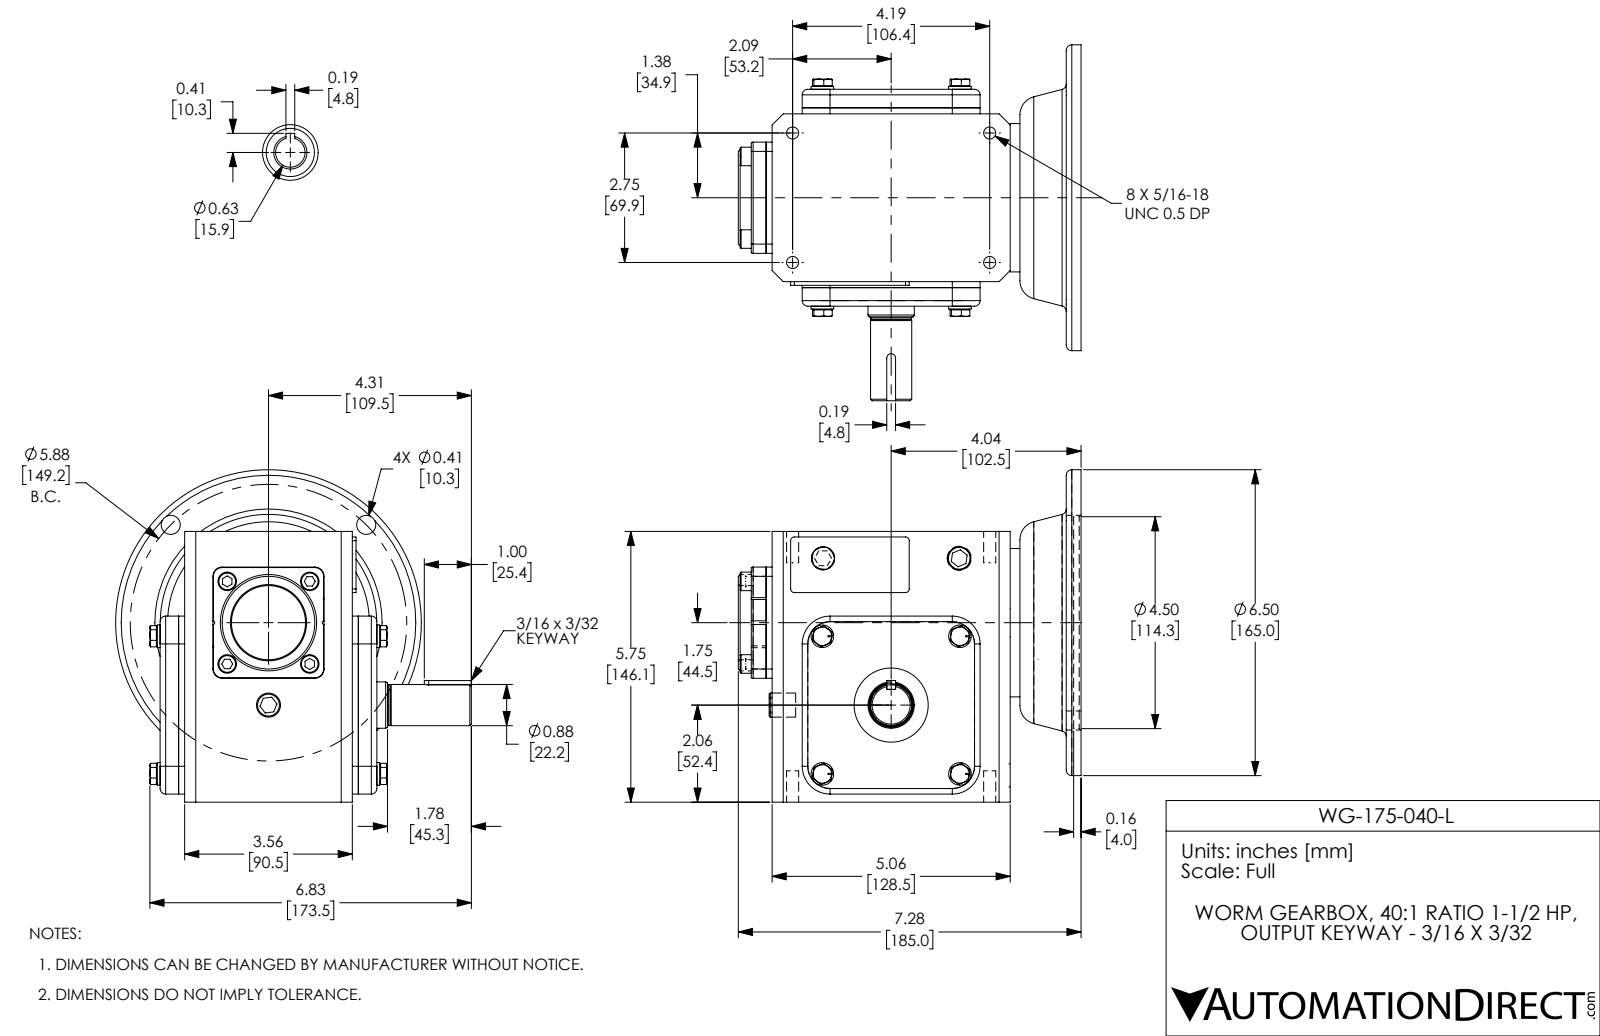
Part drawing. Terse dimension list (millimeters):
name: WG-175-040-L
written by: SolidWorks 2017 (AUTOMOTIVE_DESIGN)
unit: mm
bodies: 43 solids, 613 faces (312 planar, 172 cylindrical, 129 other)
size: 192 × 185 × 179.3
volume: 2 161 000 mm³; area: 236 400 mm²
holes: 4× ⌀6.5, 4× ⌀10.3, 1× ⌀13, 1× ⌀15.9, 1× ⌀25, 1× ⌀30, 1× ⌀37, 1× ⌀40, 1× ⌀90, 1× ⌀114.3
bosses: 8× ⌀10, 4× ⌀12.2, 2× ⌀13, 1× ⌀165, 1× ⌀80, 1× ⌀52, 1× ⌀40, 1× ⌀22.2
rounds: 8× R2, 8× R3, 4× R5, 4× R15, 2× R0.5, 2× R1, 1× R2.4
face distances: 3.3, 97, 107, 10, 13.3, 93.8, 103.8, 8, 146.1, 170
hole spacings: 74.6, 105.5, 53.4, 69.9, 106.4, 110.6, 127.3, 149.2
